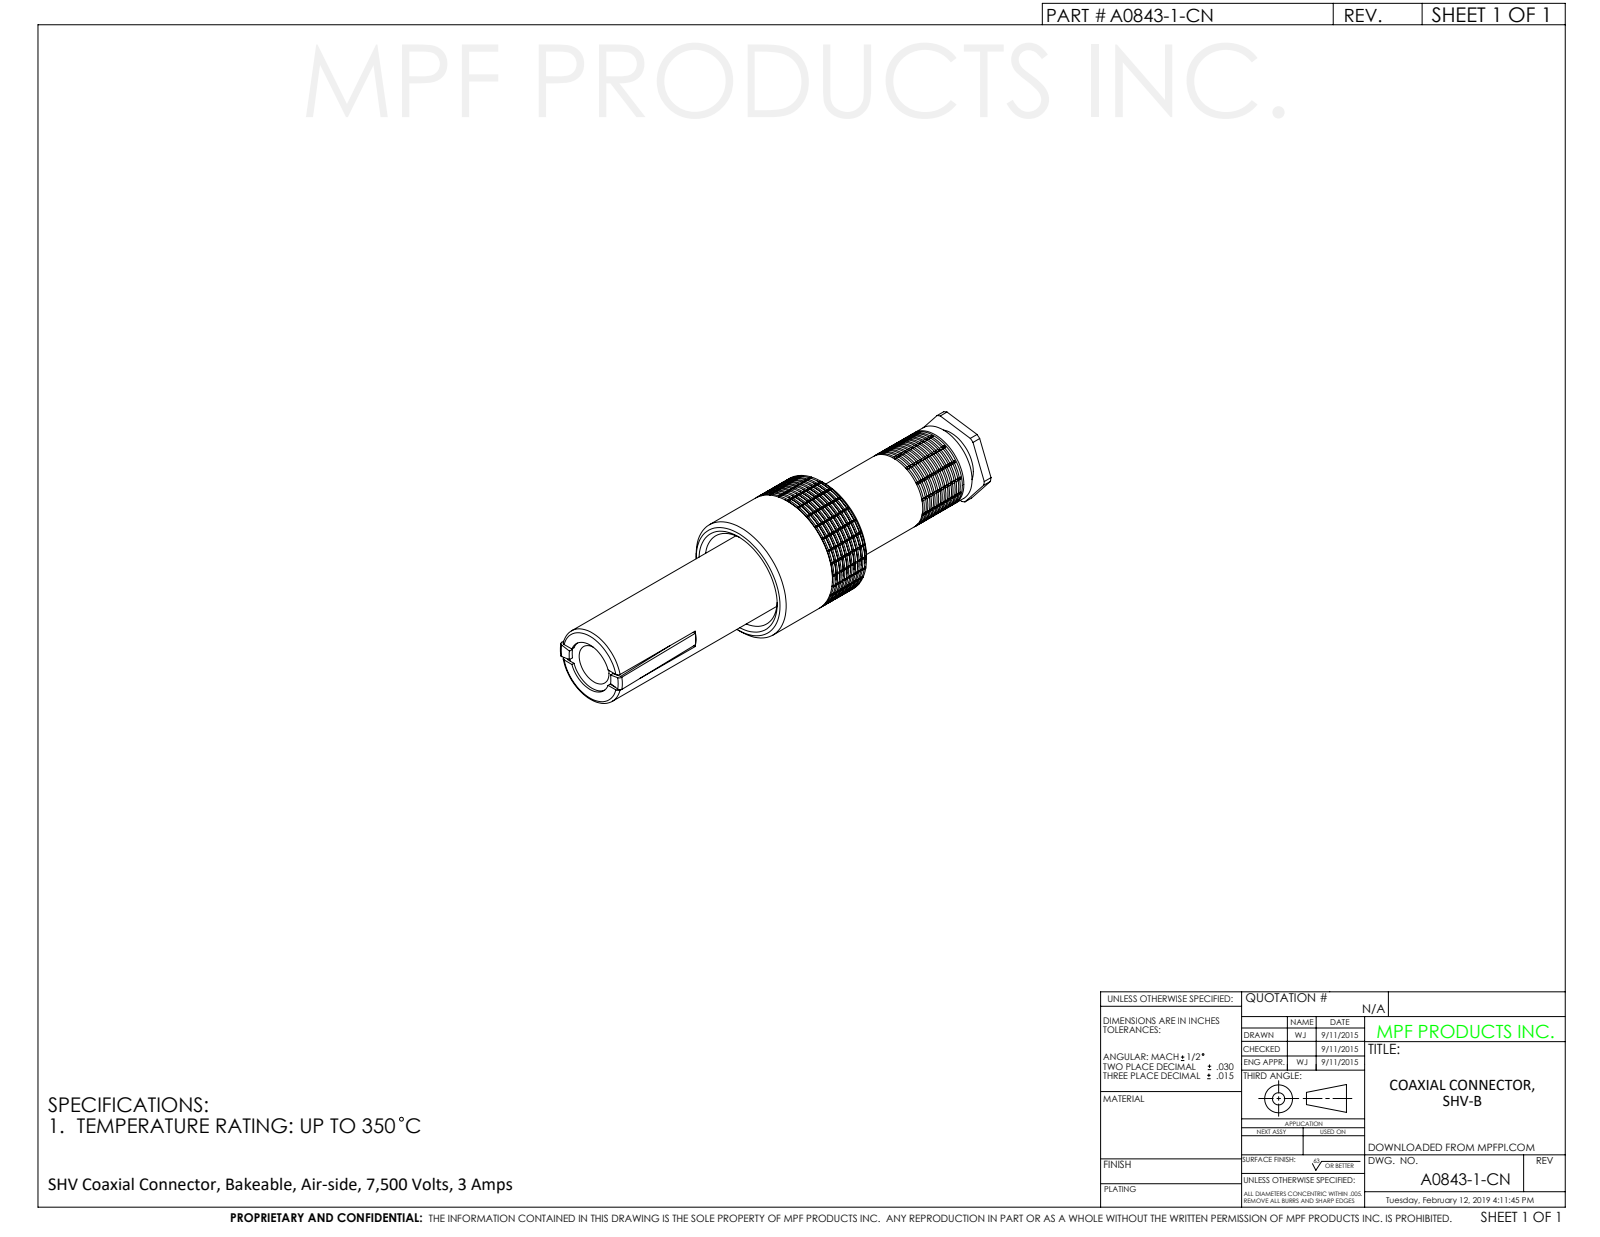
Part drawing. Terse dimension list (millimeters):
name: A0843-1-CN
written by: SolidWorks 2012 (CONFIG_CONTROL_DESIGN)
unit: mm
bodies: 1 solid, 1828 faces (485 planar, 449 cylindrical, 894 other)
size: 90.8 × 22.2 × 22.2
volume: 15 500 mm³; area: 8 806 mm²
holes: 1× ⌀7.4, 1× ⌀12.6, 1× ⌀17.8
bosses: 1× ⌀22.2, 1× ⌀22.2, 1× ⌀14.2, 1× ⌀11
rounds: 1× R4.8, 1× R5.1, 1× R5.2, 1× R8.3
face distances: 32.9, 39.5, 6.6, 1.7, 31.2, 37.9, 89.8, 88.1, 56.9, 50.3
